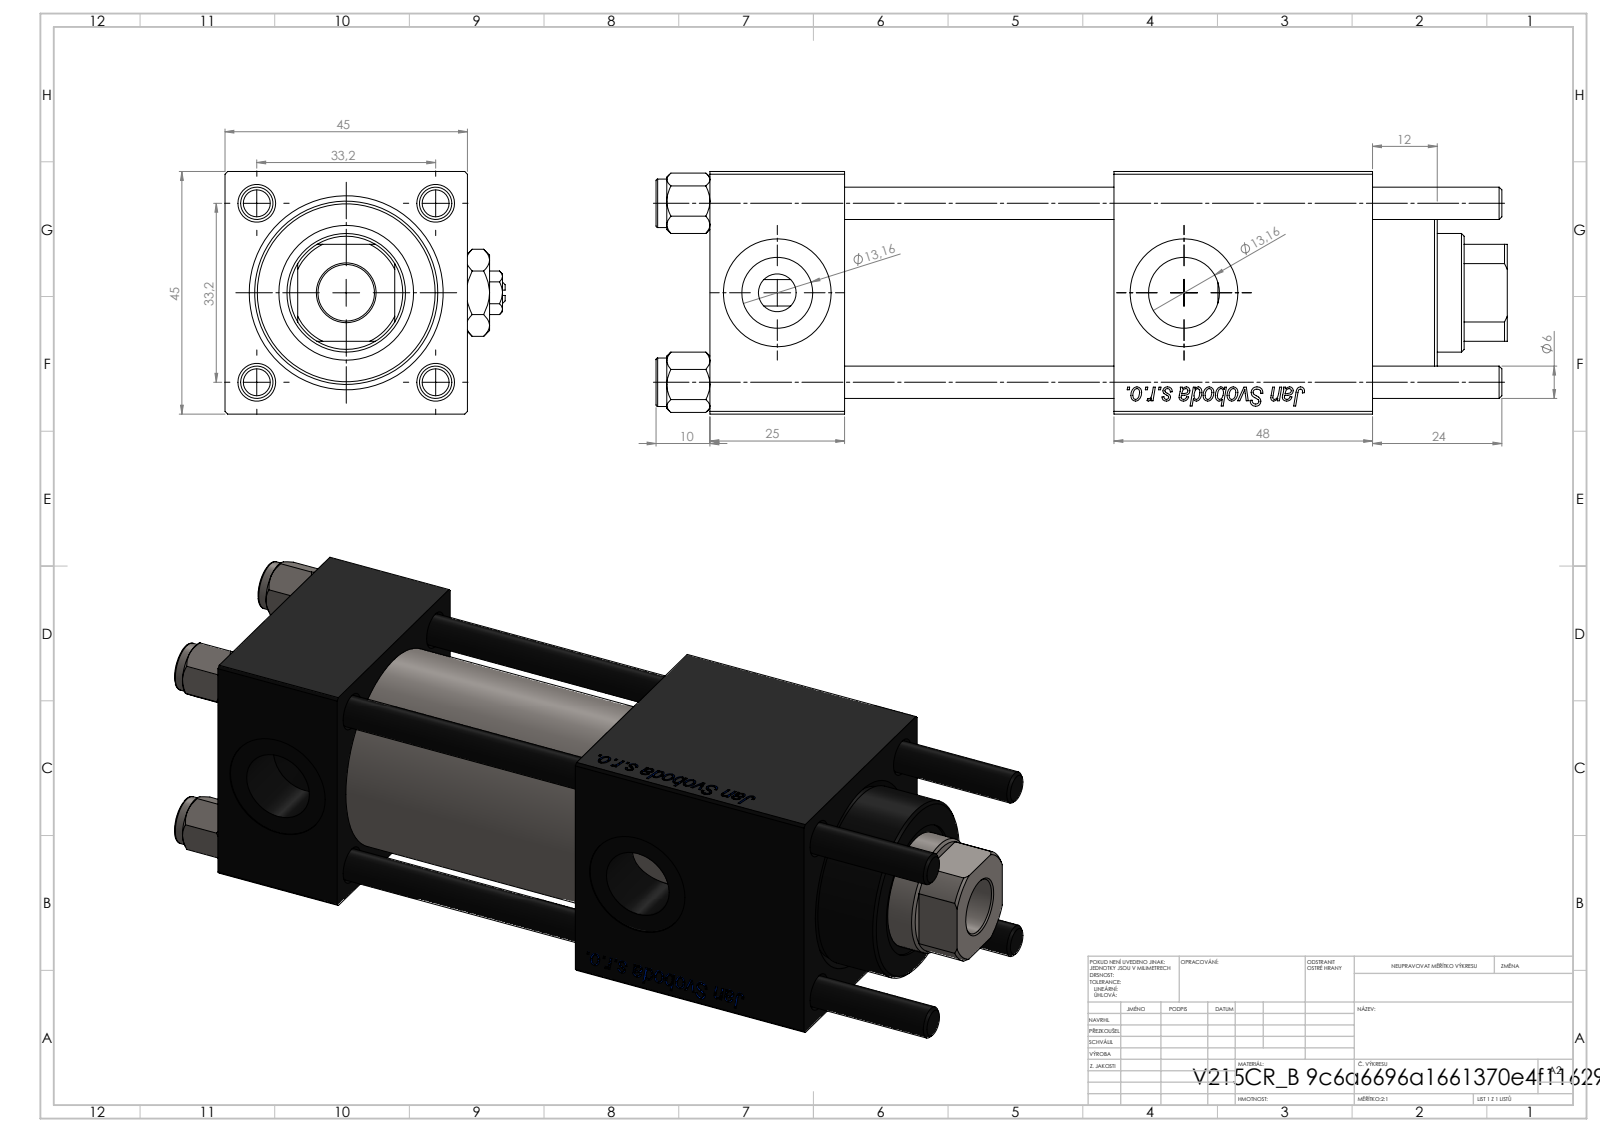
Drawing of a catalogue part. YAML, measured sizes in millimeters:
part_name: "V215CR_VCP_B; V215CR_B_TYCINKA; NUT_M5_B; V215CR_B-1 (+2 more)"
step_written_by: "SolidWorks 2019 (CONFIG_CONTROL_DESIGN)"
units: millimeters
bodies: {solids: 12, faces: 1205, planar: 455, cylindrical: 82, other: 668}
overall_size: [158, 52, 45]
volume: 213630
surface_area: 77550
round_holes:
  - {diameter: 6, count: 4}
  - {diameter: 7, count: 2}
  - {diameter: 13.16, count: 2}
  - {diameter: 20, count: 2}
  - {diameter: 10.5, count: 1}
  - {diameter: 22, count: 1}
  - {diameter: 24, count: 1}
  - {diameter: 25, count: 1}
  - {diameter: 32, count: 1}
  - {diameter: 33, count: 1}
round_bosses_or_shafts:
  - {diameter: 9, count: 4}
  - {diameter: 38, count: 1}
  - {diameter: 34, count: 1}
partial_cylinders:
  - {radius: 10.5, count: 1}
face_to_face_distances: [45, 25, 50, 123, 75, 98, 48, 94.3, 69.3, 19.3]
hole_center_spacings: [23.48, 33.2, 46.95, 75.5]
